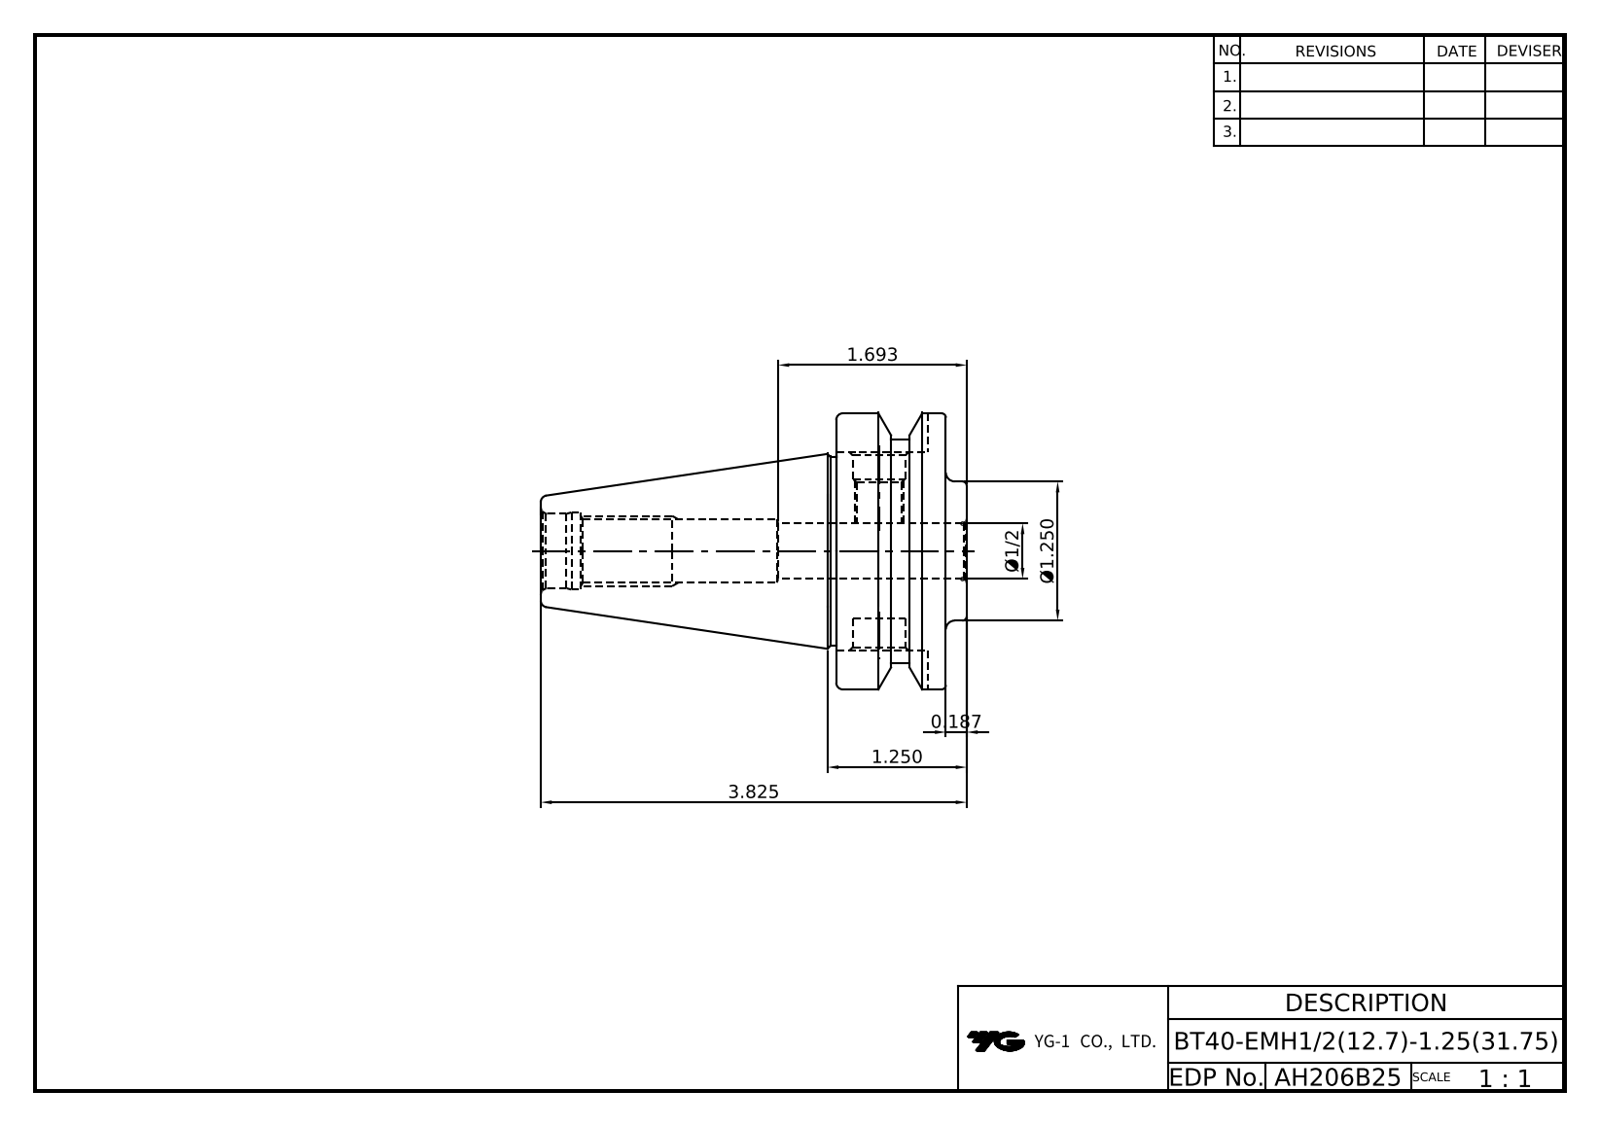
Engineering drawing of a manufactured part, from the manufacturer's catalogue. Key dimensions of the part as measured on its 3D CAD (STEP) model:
Part name (STEP PRODUCT): LO-BT40-EMH12.7-31.75
STEP written by: Autodesk Inventor 2022 (AUTOMOTIVE_DESIGN)
Units: millimetres
Bodies: 1 solid, 50 faces (17 planar, 16 cylindrical, 17 other)
Overall size (bounding box): 97.15 × 63 × 63
Volume: 120 722 mm³ · Surface area: 23 733 mm²
Round holes (diameter × count): ⌀9.73 ×1, ⌀12 ×1, ⌀12.7 ×1, ⌀13.84 ×1, ⌀17 ×1, ⌀17.6 ×1
Round bosses / shafts (diameter × count): ⌀63 ×1, ⌀51 ×1, ⌀44 ×1, ⌀31.75 ×1
Partial cylindrical surfaces — rounded edges, fillets, slot ends (radius × count): R8.05 ×1
Main face-to-face distances: 25, 29.75, 4.75, 17.1, 7.9, 12.65, 12.1, 5, 12.9, 17.65
